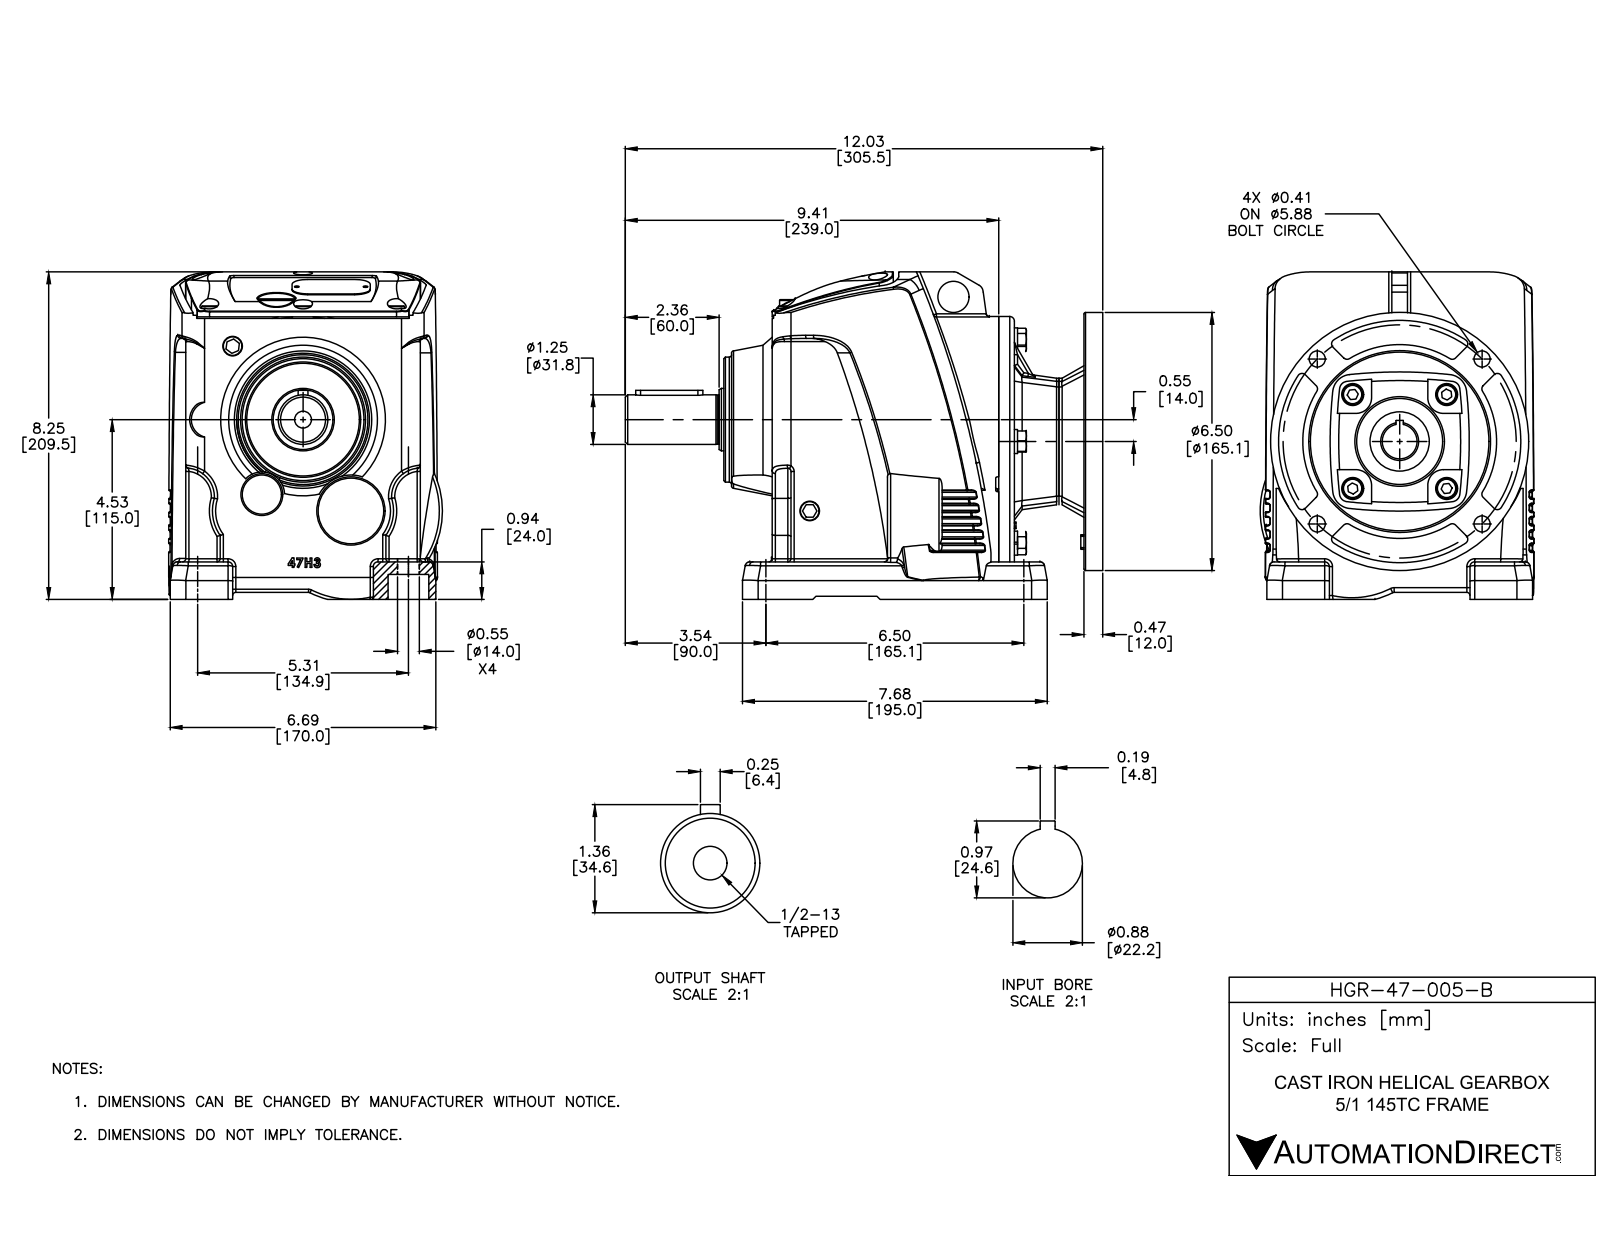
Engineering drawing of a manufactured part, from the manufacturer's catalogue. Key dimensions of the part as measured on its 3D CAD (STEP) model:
Part name (STEP PRODUCT): HGR-47-005-B
STEP written by: SolidWorks 2015 (CONFIG_CONTROL_DESIGN)
Units: inches
Bodies: 30 solids, 1143 faces (350 planar, 307 cylindrical, 486 other)
Overall size (bounding box): 12.028 × 8.248 × 6.9
Volume: 282.3 in³ · Surface area: 670.1 in²
Round holes (diameter × count): ⌀0.551 ×8, ⌀0.472 ×6, ⌀0.406 ×4, ⌀0.079 ×2, ⌀1.575 ×2, ⌀0.422 ×1, ⌀0.787 ×1, ⌀0.875 ×1, ⌀0.945 ×1, ⌀4.5 ×1
Round bosses / shafts (diameter × count): ⌀0.512 ×9, ⌀0.606 ×4, ⌀0.394 ×3, ⌀6.5 ×1, ⌀6.299 ×1, ⌀3.15 ×1, ⌀2.835 ×1, ⌀2.165 ×1
Partial cylindrical surfaces — rounded edges, fillets, slot ends (radius × count): R0.118 ×45, R0.079 ×41, R0.039 ×20, R0.394 ×12, R0.008 ×2, R0.02 ×2, R0.125 ×2, R0.197 ×2
Main face-to-face distances: 5.709, 0.276, 0.039, 0.394, 7.854, 5.118, 2.146, 1.299, 2.028, 0.472
Hole centre spacings: 3.381, 1.265, 1.673, 2.366, 2.937, 4.154, 4.611, 0.582
